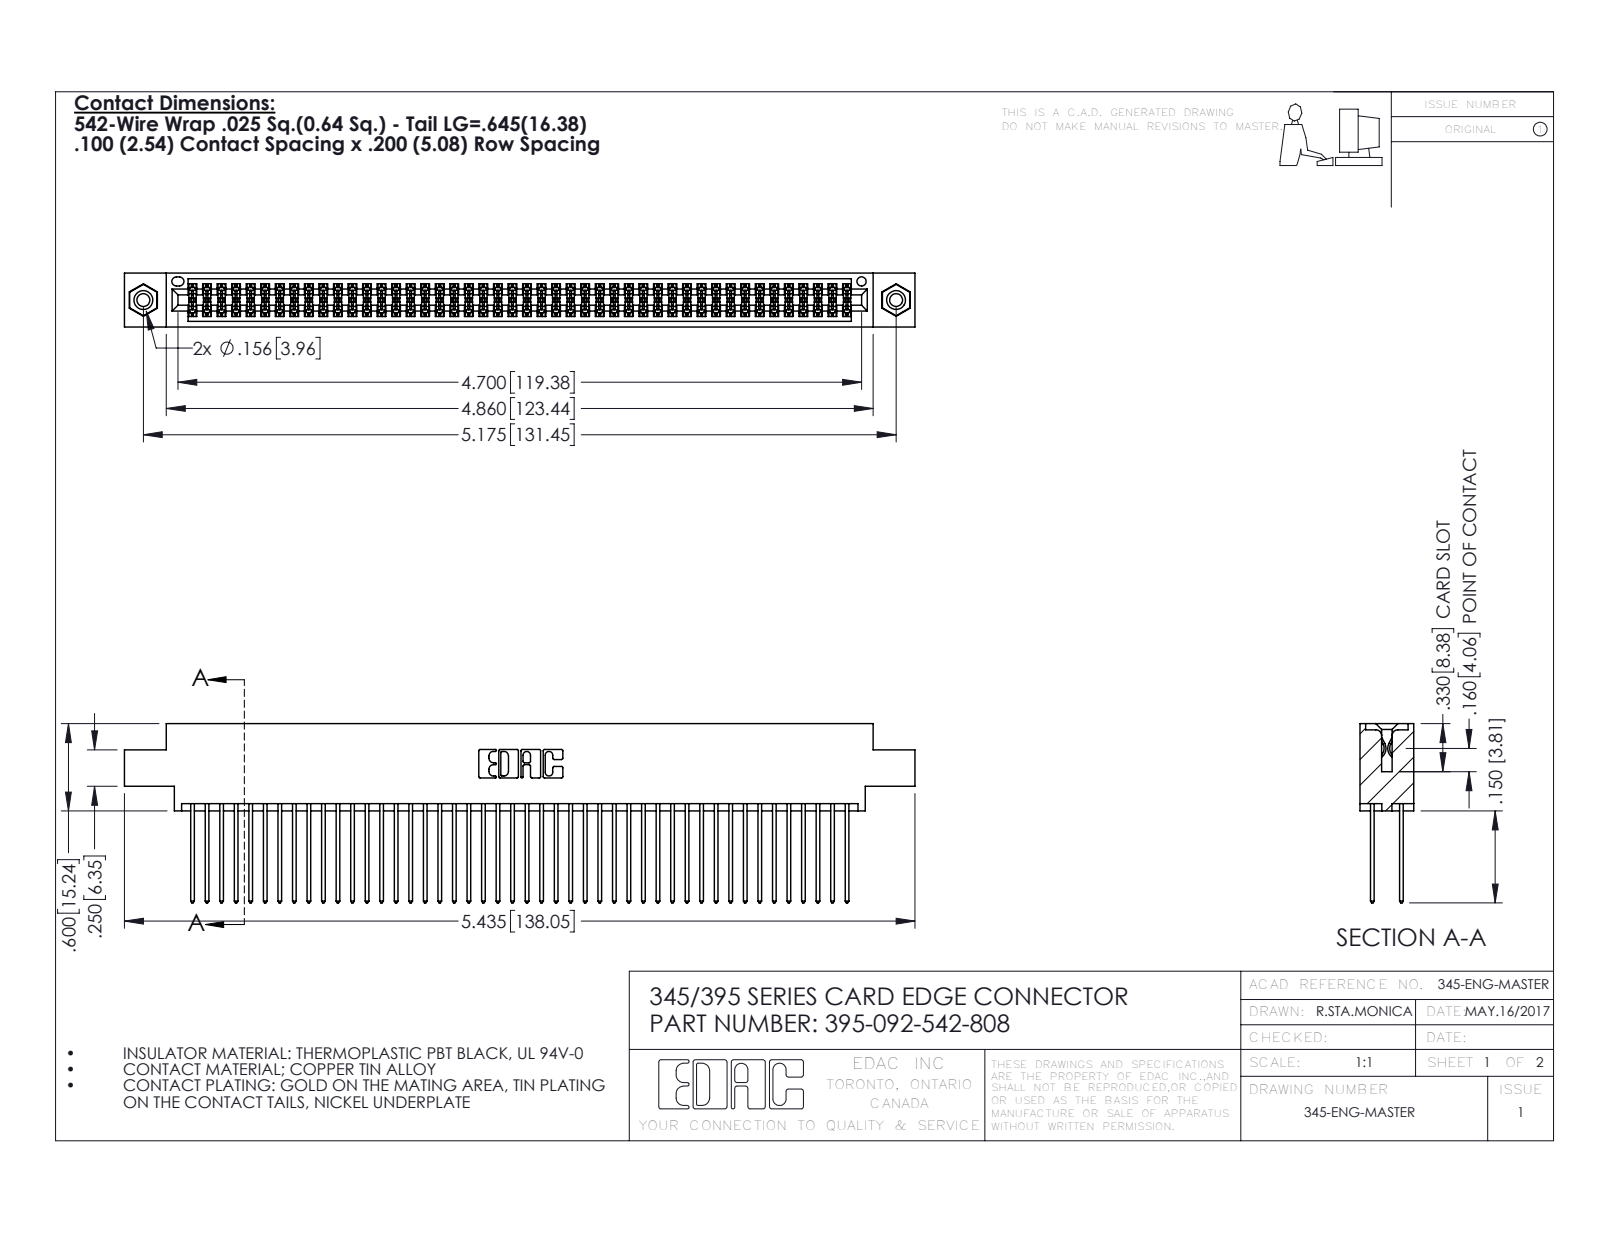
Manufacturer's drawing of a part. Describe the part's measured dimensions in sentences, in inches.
The part is named "345 Part_0.170 Offset - 0.156 Dia-TI; 345-250-001_345-250-003-102; 395-092-542-808; 345-292-001_345-293-142". Its 3-D file was written by "SolidWorks 2016 (CONFIG_CONTROL_DESIGN)". It is 95 solids with 4790 faces: 3152 planar, 1622 cylindrical and 16 other. Overall it measures 5.435 by 1.232 by 0.37 inches. Its volume is 0.839 cubic inches and its surface area 34.99 square inches. Round holes: 2 of diameter 0.089, 2 of diameter 0.125, 2 of diameter 0.156, 1 of diameter 0.064. Round bosses or shafts: 2 of diameter 0.155. Partial cylindrical surfaces (rounded edges, fillets, slot ends): 138 of radius 0.006, 92 of radius 0.01, 22 of radius 0.01, 6 of radius 0.007, 6 of radius 0.031, 3 of radius 0.026, 2 of radius 0.014, 2 of radius 0.019. The main face-to-face distances are 0.072, 0.298, 0.2, 0.098, 0.272, 0.025, 0.37, 0.225, 0.175, 0.149. The hole center spacings are 0.27, 4.939, 5.175.
